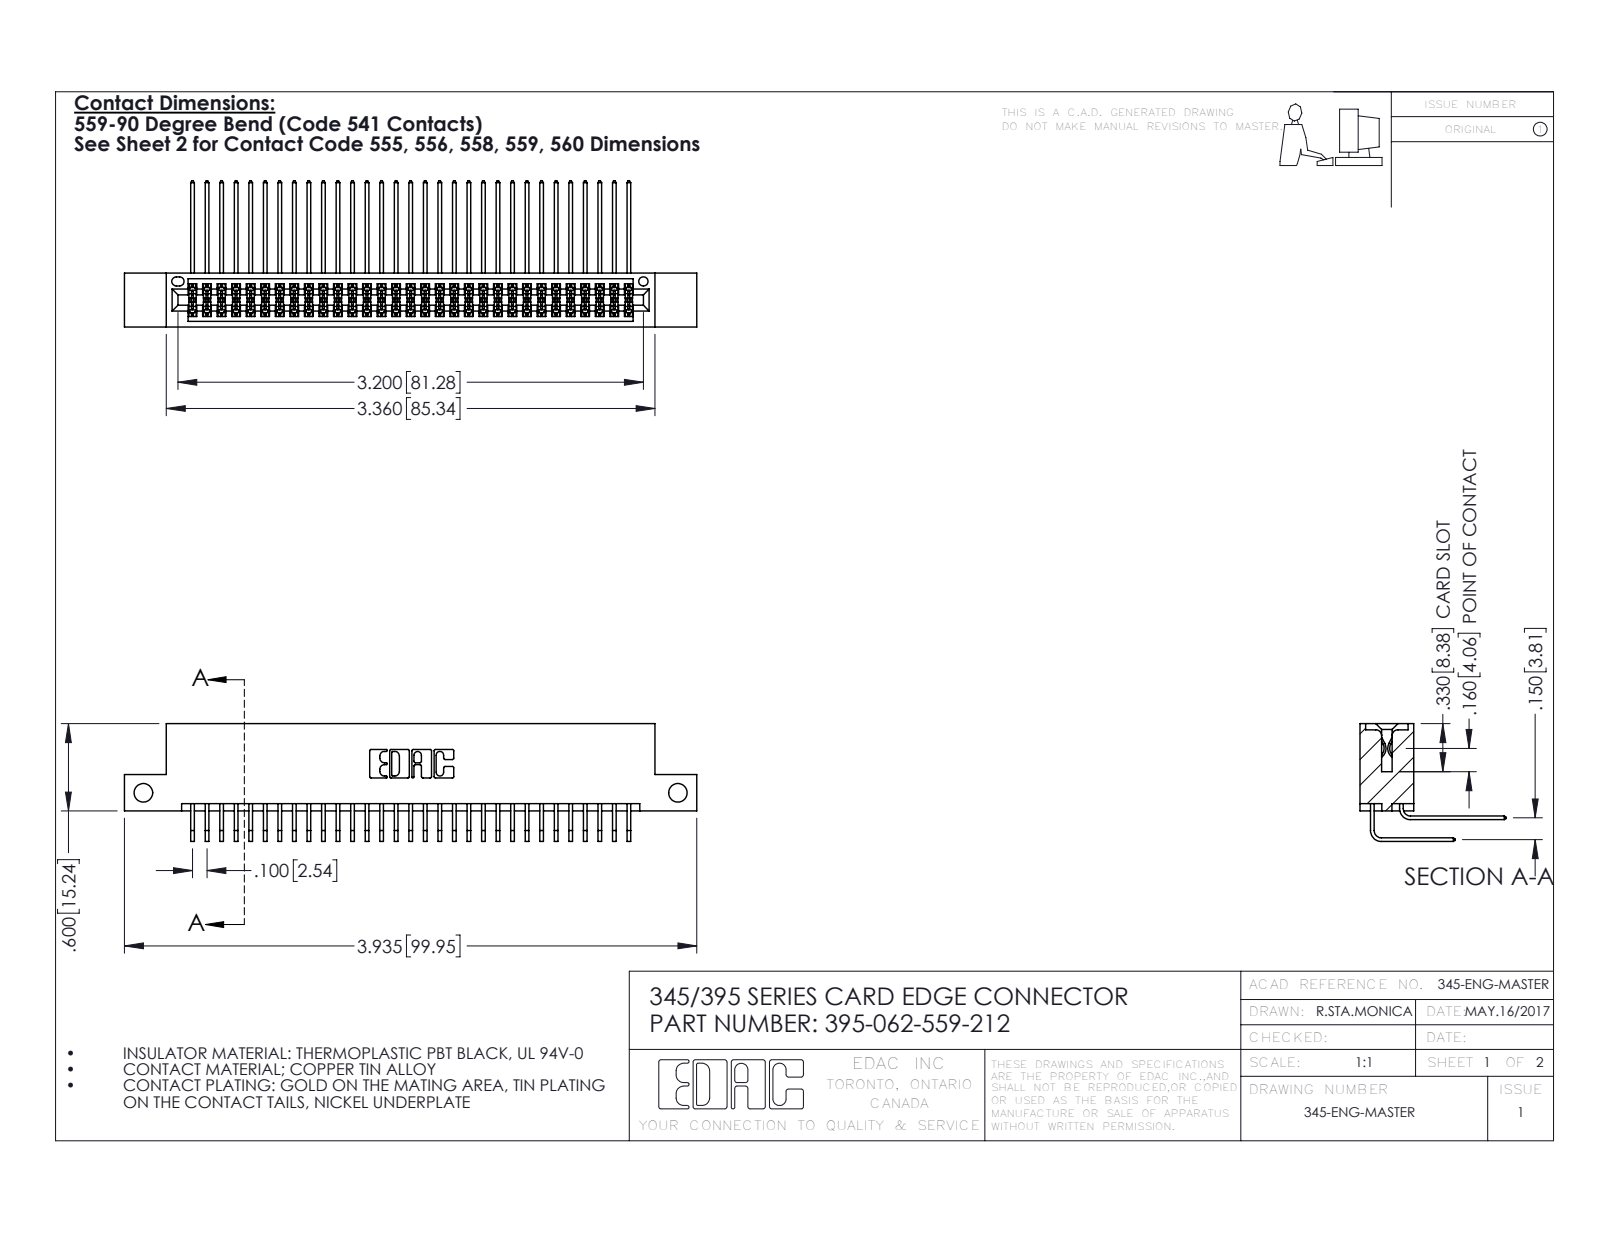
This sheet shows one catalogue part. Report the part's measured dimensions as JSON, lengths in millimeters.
{"part_name": "395-062-559-212; 345-292-001_558 559 Tail - 1; 345 Part_Flush Mounting Lugs - Side Mount; 345-292-001_559 Tail - 2", "step_written_by": "SolidWorks 2016 (CONFIG_CONTROL_DESIGN)", "units": "millimeters", "bodies": {"solids": 63, "faces": 3350, "planar": 2250, "cylindrical": 1100, "other": 0}, "overall_size": [99.9, 25.5, 20.5], "volume_mm3": 9880, "surface_area_mm2": 15940, "round_holes": [[3.3, 2], [1.6, 1]], "partial_cylinders_radius": [[0.2, 94], [0.3, 22], [0.2, 6], [0.8, 6], [0.7, 3], [0.4, 2], [0.5, 2], [0.6, 2]], "face_to_face_distances": [1.8, 7.6, 5.1, 9.4, 2.5, 6.9, 0.6, 5.7, 3.8, 4.4], "hole_center_spacings": [93.3]}
